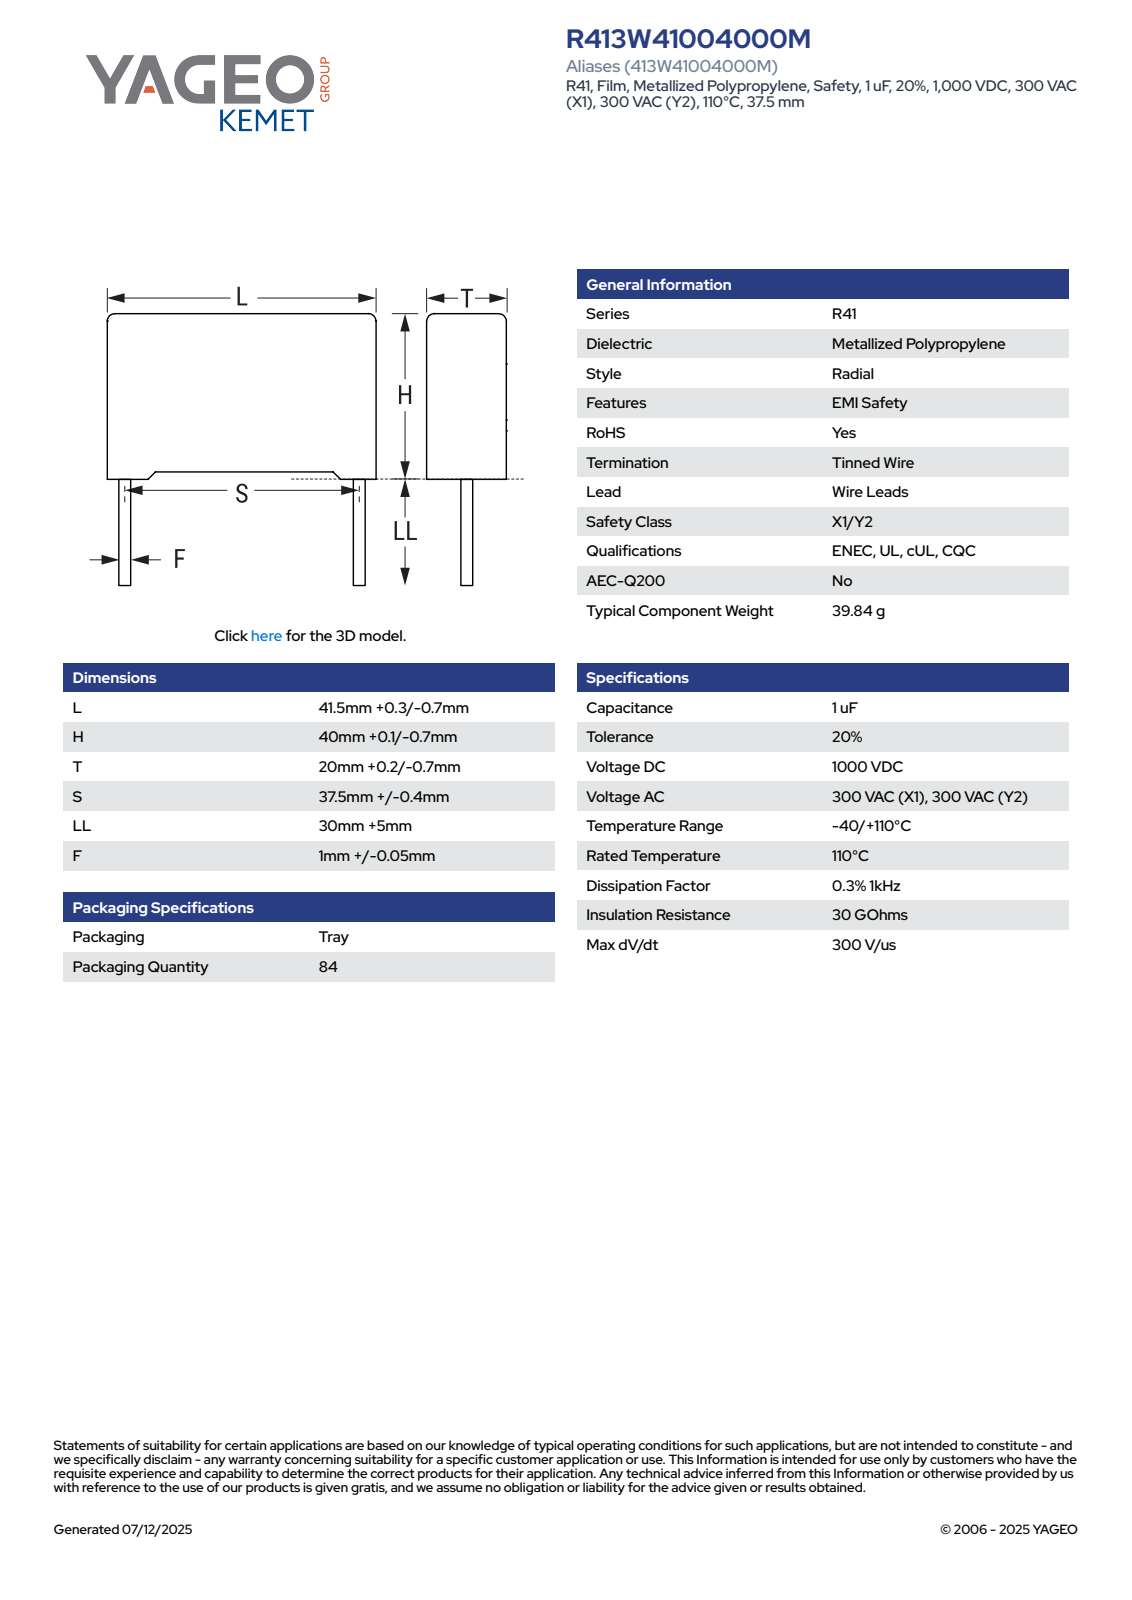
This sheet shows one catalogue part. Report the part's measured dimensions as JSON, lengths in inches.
{"part_name": "CFR_RB2_41.5X40X20_L41.8H40.1T20.2S37.5LL35F1.05", "step_written_by": "SolidWorks 2021 (AUTOMOTIVE_DESIGN)", "units": "inches", "bodies": {"solids": 4, "faces": 85, "planar": 77, "cylindrical": 8, "other": 0}, "overall_size": [2.957, 1.646, 0.795], "volume_in3": 2.009, "surface_area_in2": 10.78, "round_bosses_or_shafts": [[0.041, 2]], "partial_cylinders_radius": [[0.02, 4]], "face_to_face_distances": [0.795, 1.646, 1.524, 0.025, 1.549, 0.03, 0.054, 1.579, 0.055, 0.796]}
